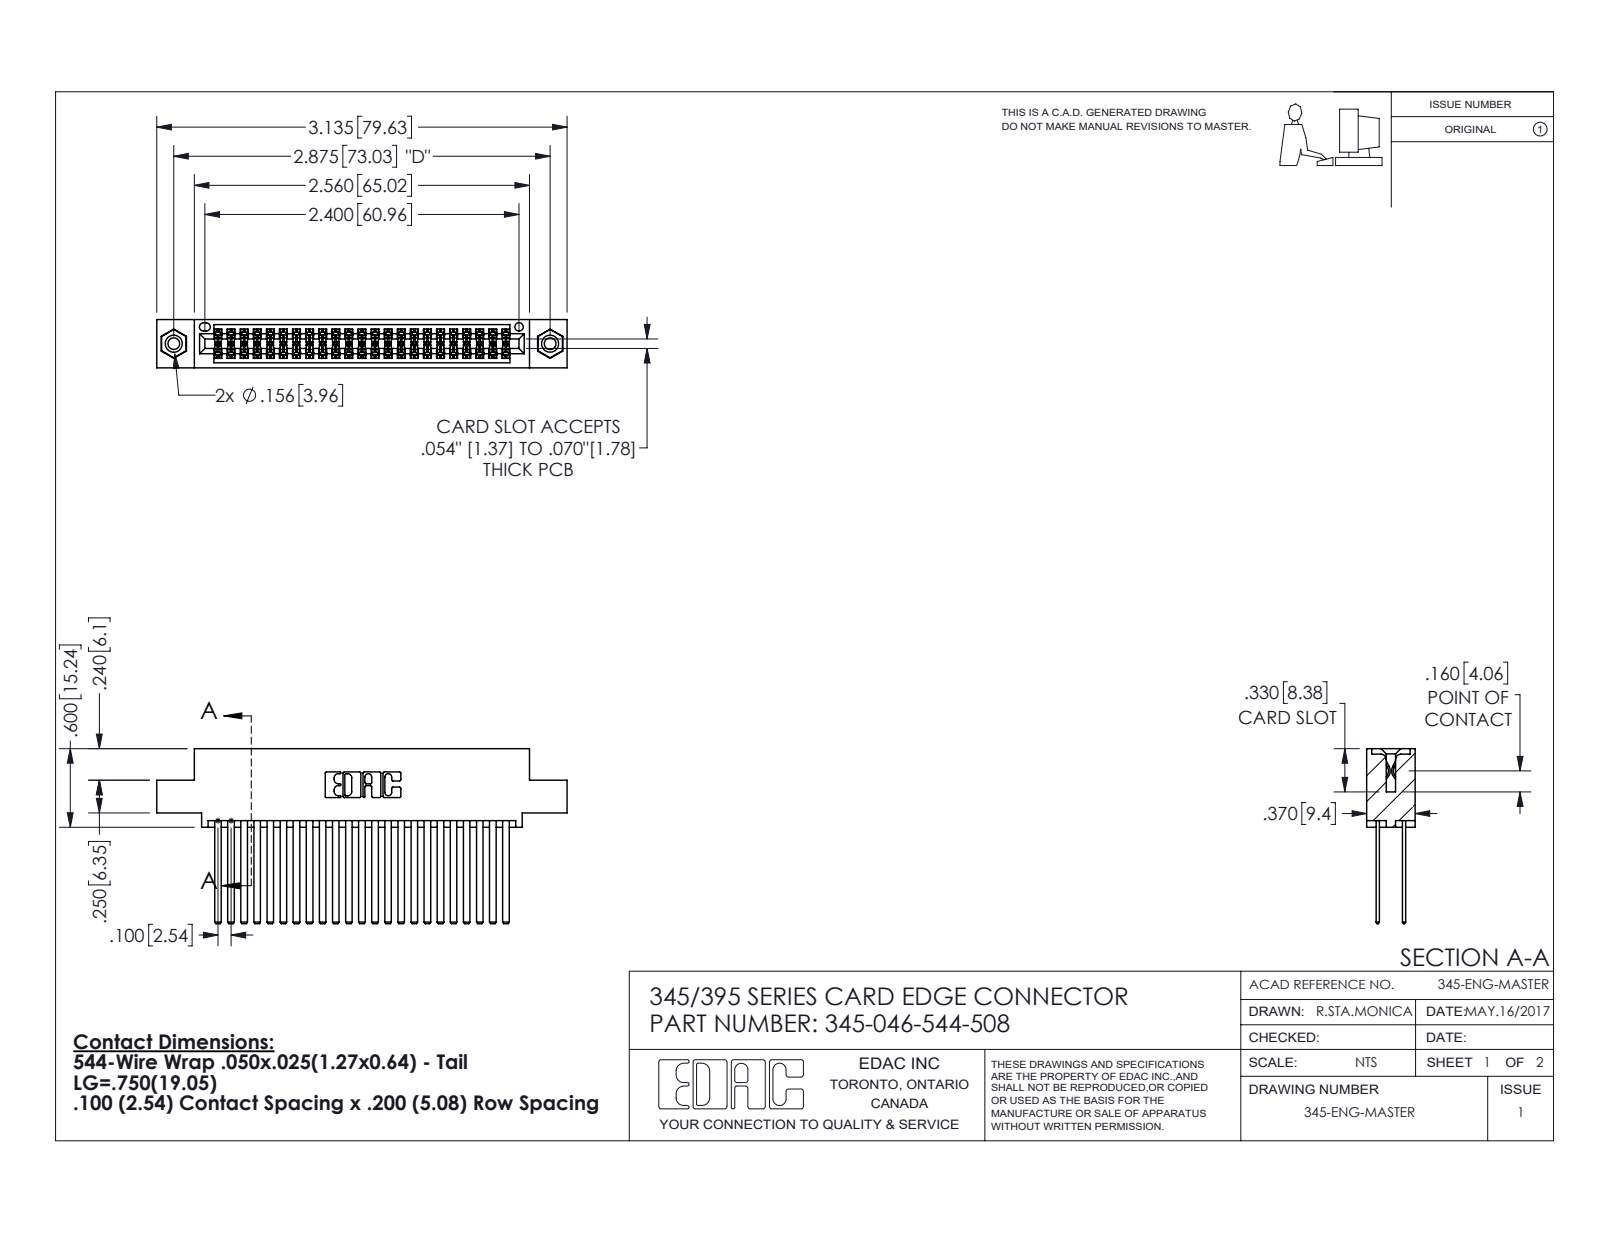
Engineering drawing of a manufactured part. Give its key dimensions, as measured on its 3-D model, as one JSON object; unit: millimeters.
{"part_name": "345-250-001_345-250-003-102; 345 Part_0.110 Offset - 0.156 Dia-TI; 345-292-001_345-293-144; 345-046-544-508", "step_written_by": "SolidWorks 2016 (CONFIG_CONTROL_DESIGN)", "units": "millimeters", "bodies": {"solids": 49, "faces": 2214, "planar": 1450, "cylindrical": 748, "other": 16}, "overall_size": [79.6, 34, 9.4], "volume_mm3": 8130, "surface_area_mm2": 13640, "round_holes": [[2.3, 2], [3.2, 2], [4, 2], [1.6, 1]], "round_bosses_or_shafts": [[3.9, 2]], "partial_cylinders_radius": [[0.2, 69], [0.3, 22], [0.2, 6], [0.8, 6], [0.7, 3], [0.4, 2], [0.5, 2], [0.6, 2]], "face_to_face_distances": [5.1, 1.8, 7.6, 0.6, 2.5, 6.9, 5.7, 4.4, 9.4, 1.3], "hole_center_spacings": [6.9, 67.1, 73]}
